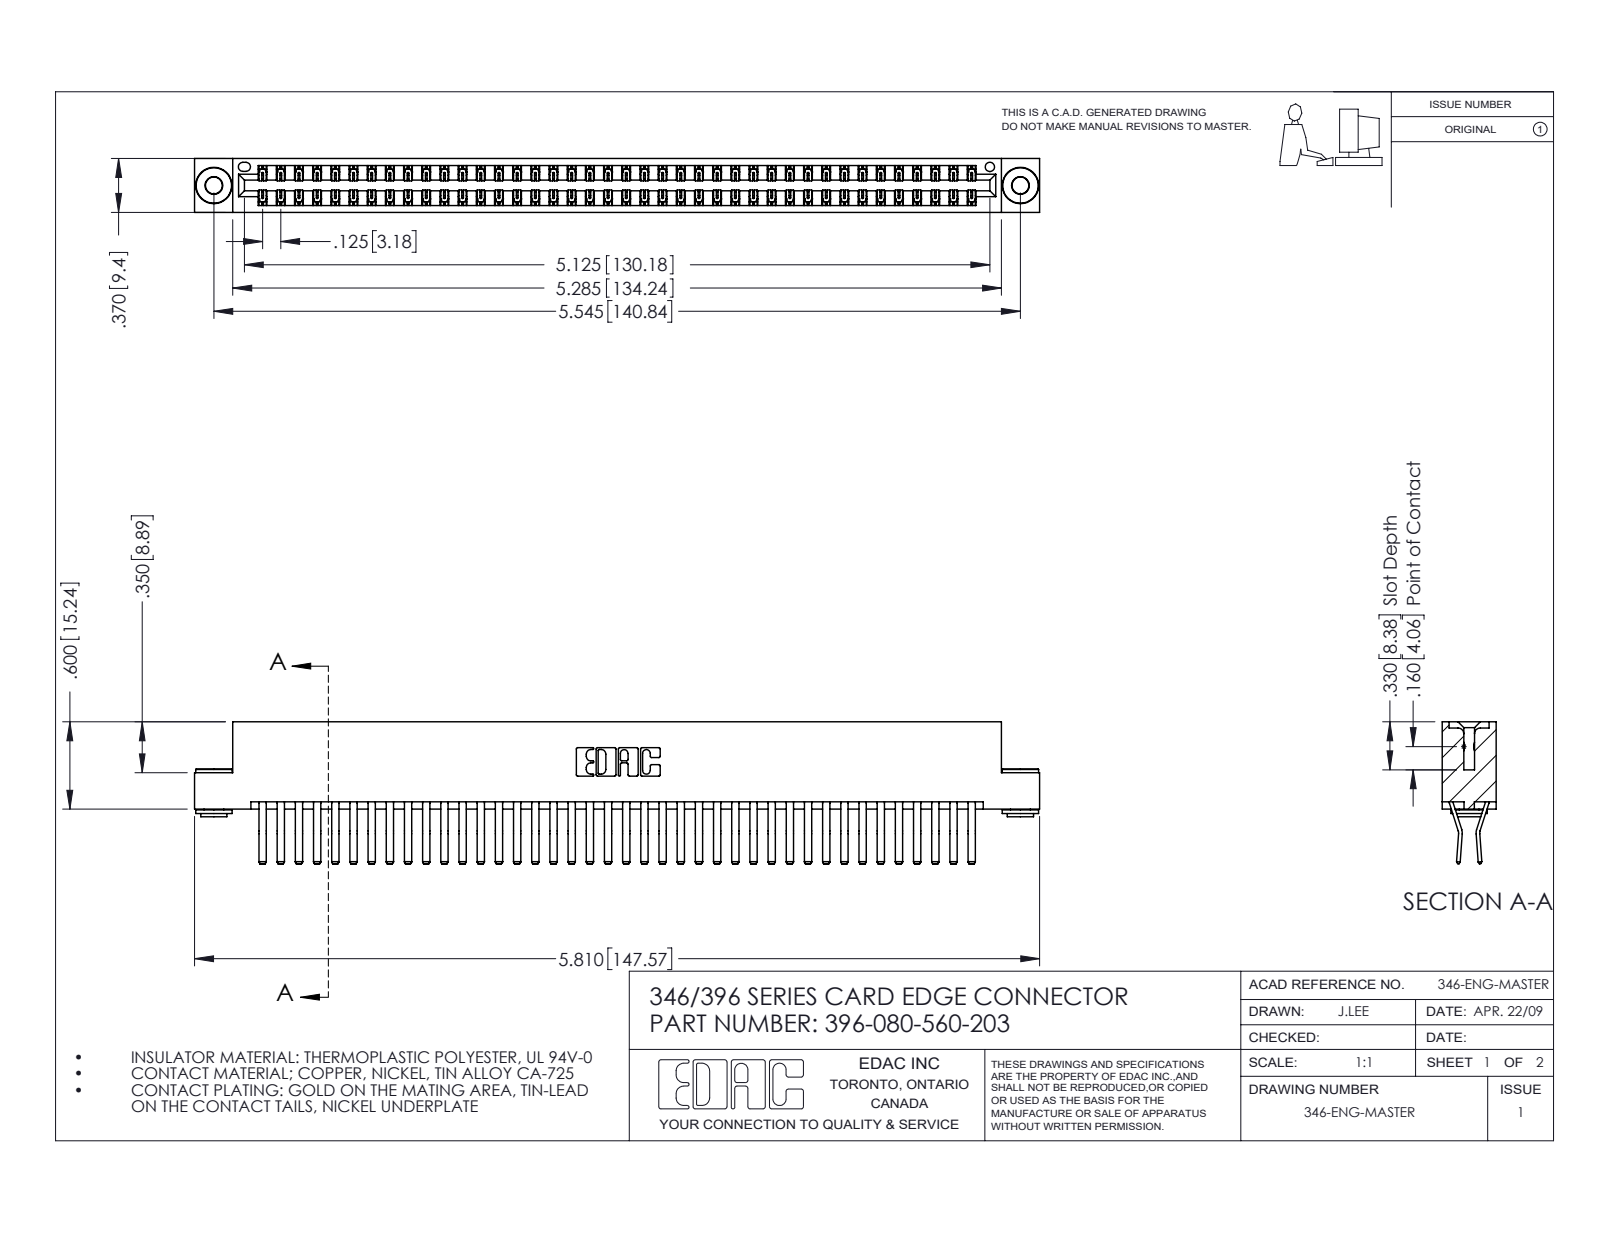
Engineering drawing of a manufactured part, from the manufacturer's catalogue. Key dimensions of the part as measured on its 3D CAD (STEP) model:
Part name (STEP PRODUCT): 396-080-560-203; 345-250-002_345-250-002-102; 345-292-001_560 Tail; 346 Part_Flush Mounting Lugs - 0.156 Dia-TH
STEP written by: SolidWorks 2016 (CONFIG_CONTROL_DESIGN)
Units: inches
Bodies: 83 solids, 4480 faces (2886 planar, 1586 cylindrical, 8 other)
Overall size (bounding box): 5.81 × 0.975 × 0.37
Volume: 0.91 in³ · Surface area: 34.24 in²
Round holes (diameter × count): ⌀0.116 ×2, ⌀0.156 ×2, ⌀0.064 ×1
Round bosses / shafts (diameter × count): ⌀0.25 ×2, ⌀0.18 ×2, ⌀0.136 ×2
Partial cylindrical surfaces — rounded edges, fillets, slot ends (radius × count): R0.006 ×120, R0.01 ×22, R0.007 ×6, R0.031 ×6, R0.026 ×3, R0.01 ×2, R0.014 ×2, R0.022 ×2
Main face-to-face distances: 0.048, 0.322, 0.37, 0.025, 0.25, 0.072, 0.298, 0.275, 0.148, 0.222
Hole centre spacings: 0.246, 5.336, 5.545
